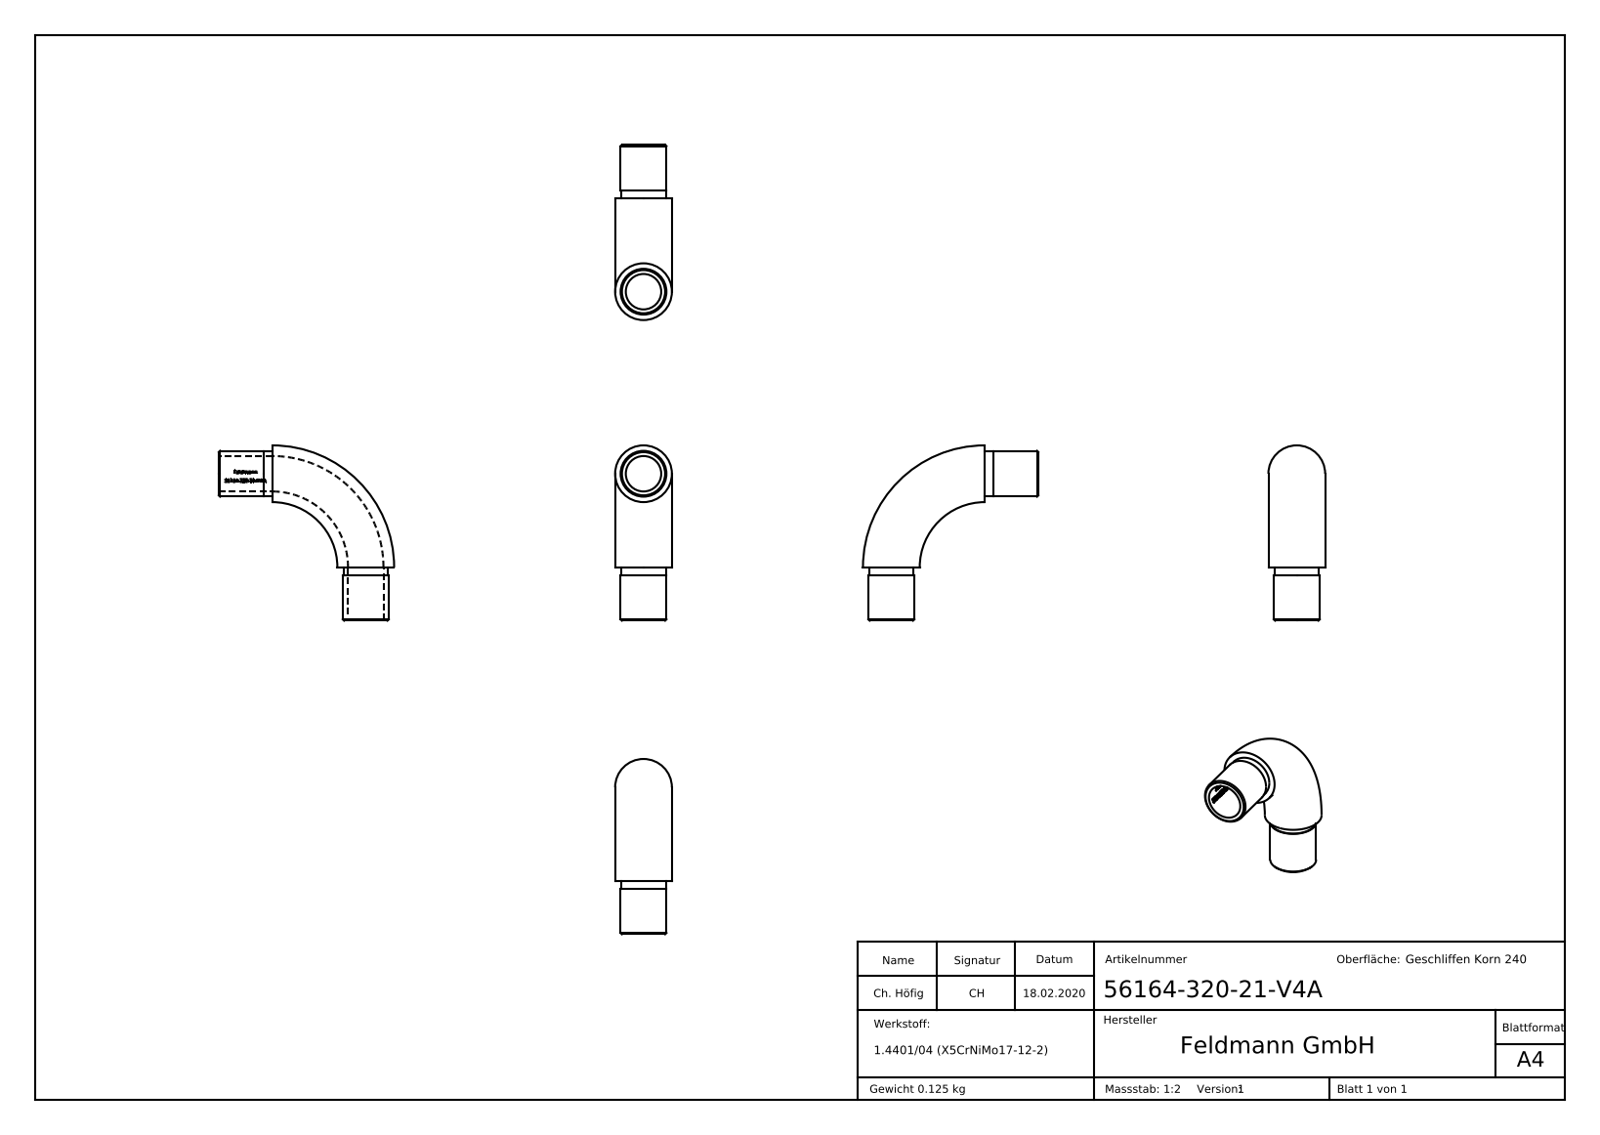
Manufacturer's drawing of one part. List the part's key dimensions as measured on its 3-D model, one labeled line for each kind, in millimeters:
Part name (STEP PRODUCT): 56164-320-21-V4A
STEP written by: SolidWorks 2015 (CONFIG_CONTROL_DESIGN)
Units: millimetres
Bodies: 1 solid, 307 faces (155 planar, 39 cylindrical, 113 other)
Overall size (bounding box): 65.8 × 65.8 × 21.3
Volume: 15 662 mm³ · Surface area: 10 285 mm²
Round holes (diameter × count): ⌀13.3 ×2
Round bosses / shafts (diameter × count): ⌀17.2 ×2, ⌀16.8 ×2
Partial cylindrical surfaces — rounded edges, fillets, slot ends (radius × count): R6.75 ×1
Main face-to-face distances: 20, 3, 17, 0.44, 2.97, 3.2, 1.19, 3.24, 1.18, 51.95
